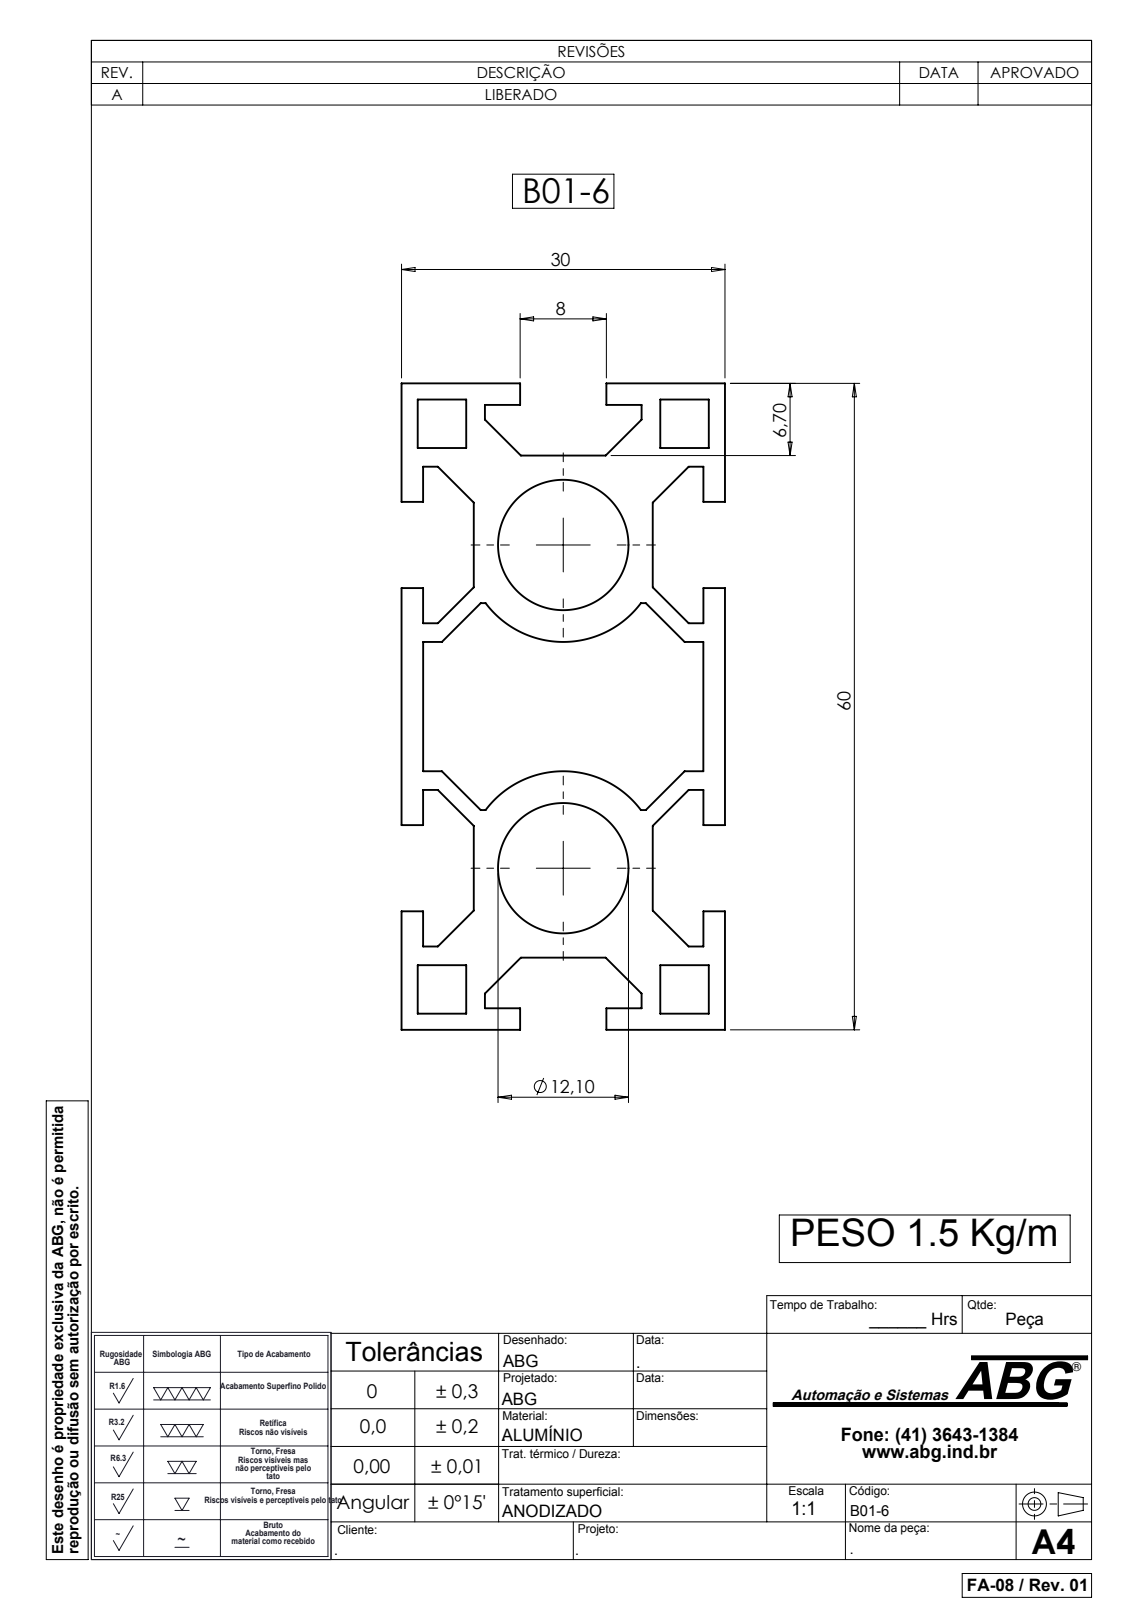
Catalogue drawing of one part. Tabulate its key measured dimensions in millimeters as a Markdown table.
| quantity | value |
| --- | --- |
| part name | B01-6 |
| STEP written by | SolidWorks 2007 (CONFIG_CONTROL_DESIGN) |
| units | millimeters |
| bodies | 1 solid, 102 faces (96 planar, 6 cylindrical, 0 other) |
| overall size | 6000 × 60 × 30 |
| volume | 4 046 000 mm³ |
| surface area | 3 301 000 mm² |
| round holes (diameter × count) | 12.1 × 2 |
| partial cylindrical surfaces (radius × count) | 9 × 2 |
| main face-to-face distances | 30, 6.7, 2, 4.7, 1.5, 6, 4.5, 5.2, 0.7, 23.3 |
| hole center spacings | 30 |
